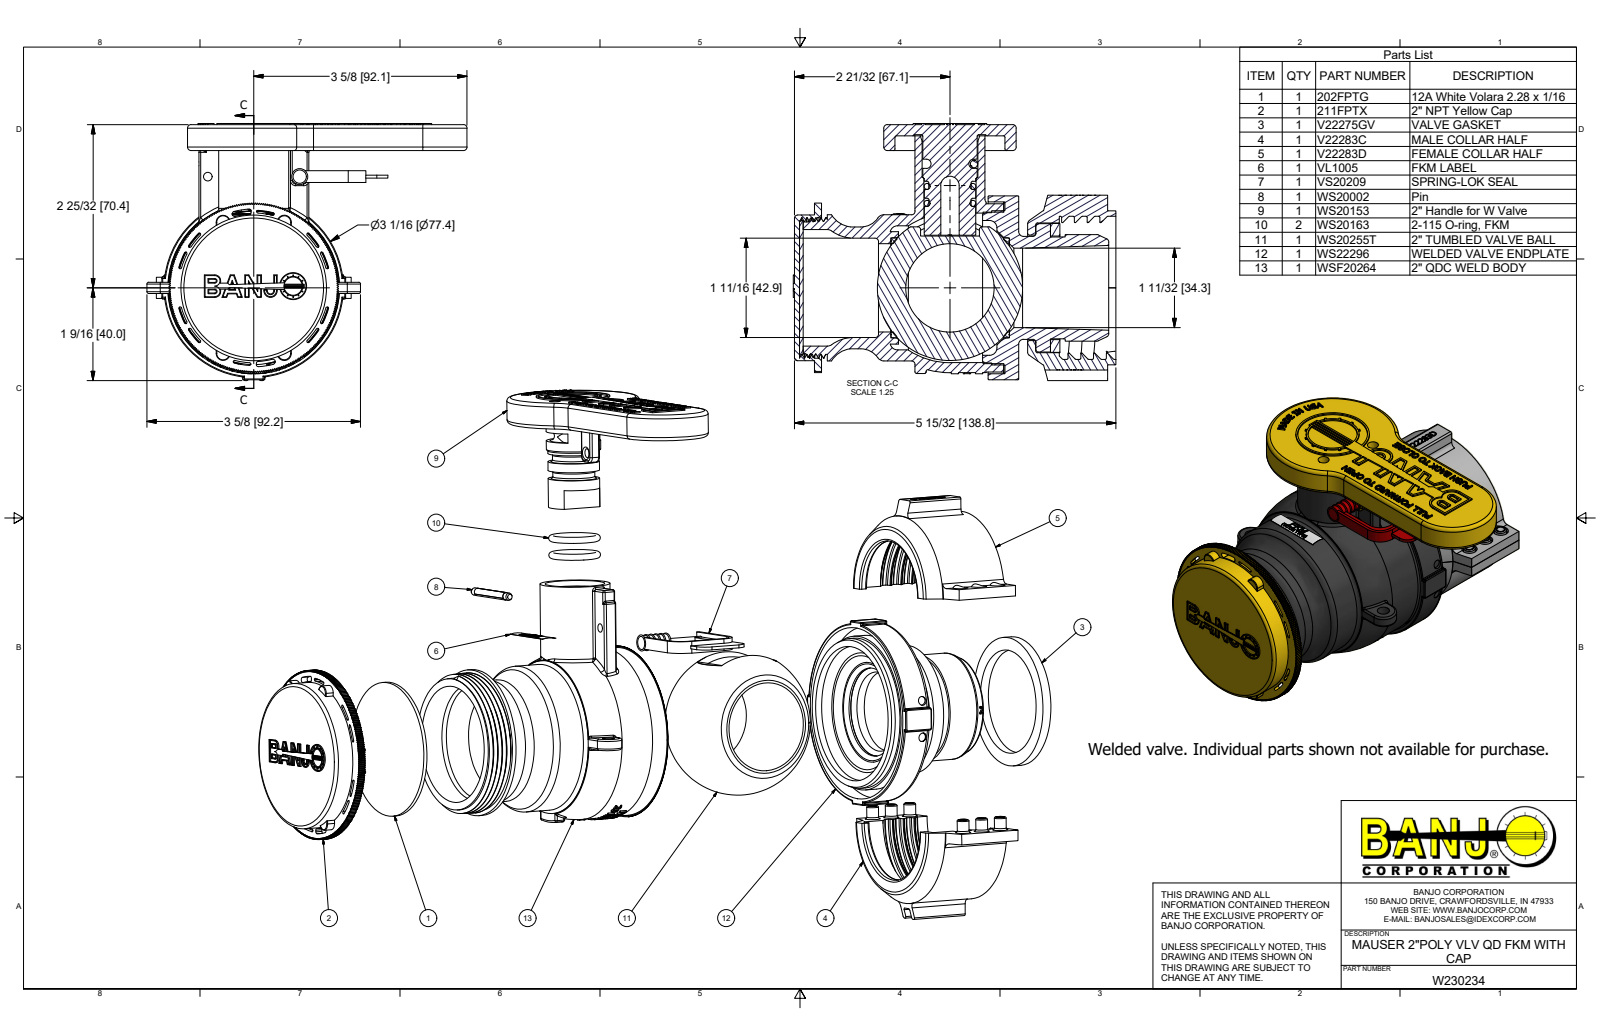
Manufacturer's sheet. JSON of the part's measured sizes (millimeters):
{"part_name": "W230234; WSF20264; WSF20264X; V22275GV (+8 more)", "step_written_by": "Autodesk Inventor 2018 (AUTOMOTIVE_DESIGN)", "units": "millimeters", "bodies": {"solids": 17, "faces": 3961, "planar": 1970, "cylindrical": 955, "other": 1036}, "overall_size": [139.3, 138.2, 110.9], "volume_mm3": 332300, "surface_area_mm2": 164600, "round_holes": [[5.3, 6], [6.5, 6], [3.7, 2], [3.8, 2], [4.8, 2], [5.3, 2], [38.1, 2], [4, 1], [7.8, 1], [7.9, 1], [11.1, 1], [21.3, 1]], "round_bosses_or_shafts": [[5.1, 6], [77.4, 1], [74.2, 1], [73.9, 1], [73.2, 1], [72.6, 1], [66.5, 1], [66.4, 1]], "partial_cylinders_radius": [[0.8, 68], [0.4, 24], [2.3, 10], [1.5, 4], [3, 4], [6.4, 4], [0.3, 3], [1.8, 3]], "face_to_face_distances": [1.6, 2.2, 4.8, 3.8, 93.1, 94.7, 96.8, 6.4, 0.5, 13.7], "hole_center_spacings": [73.2, 72.6, 9.5, 9.5, 19.1, 27.2, 41.5, 51.9]}
